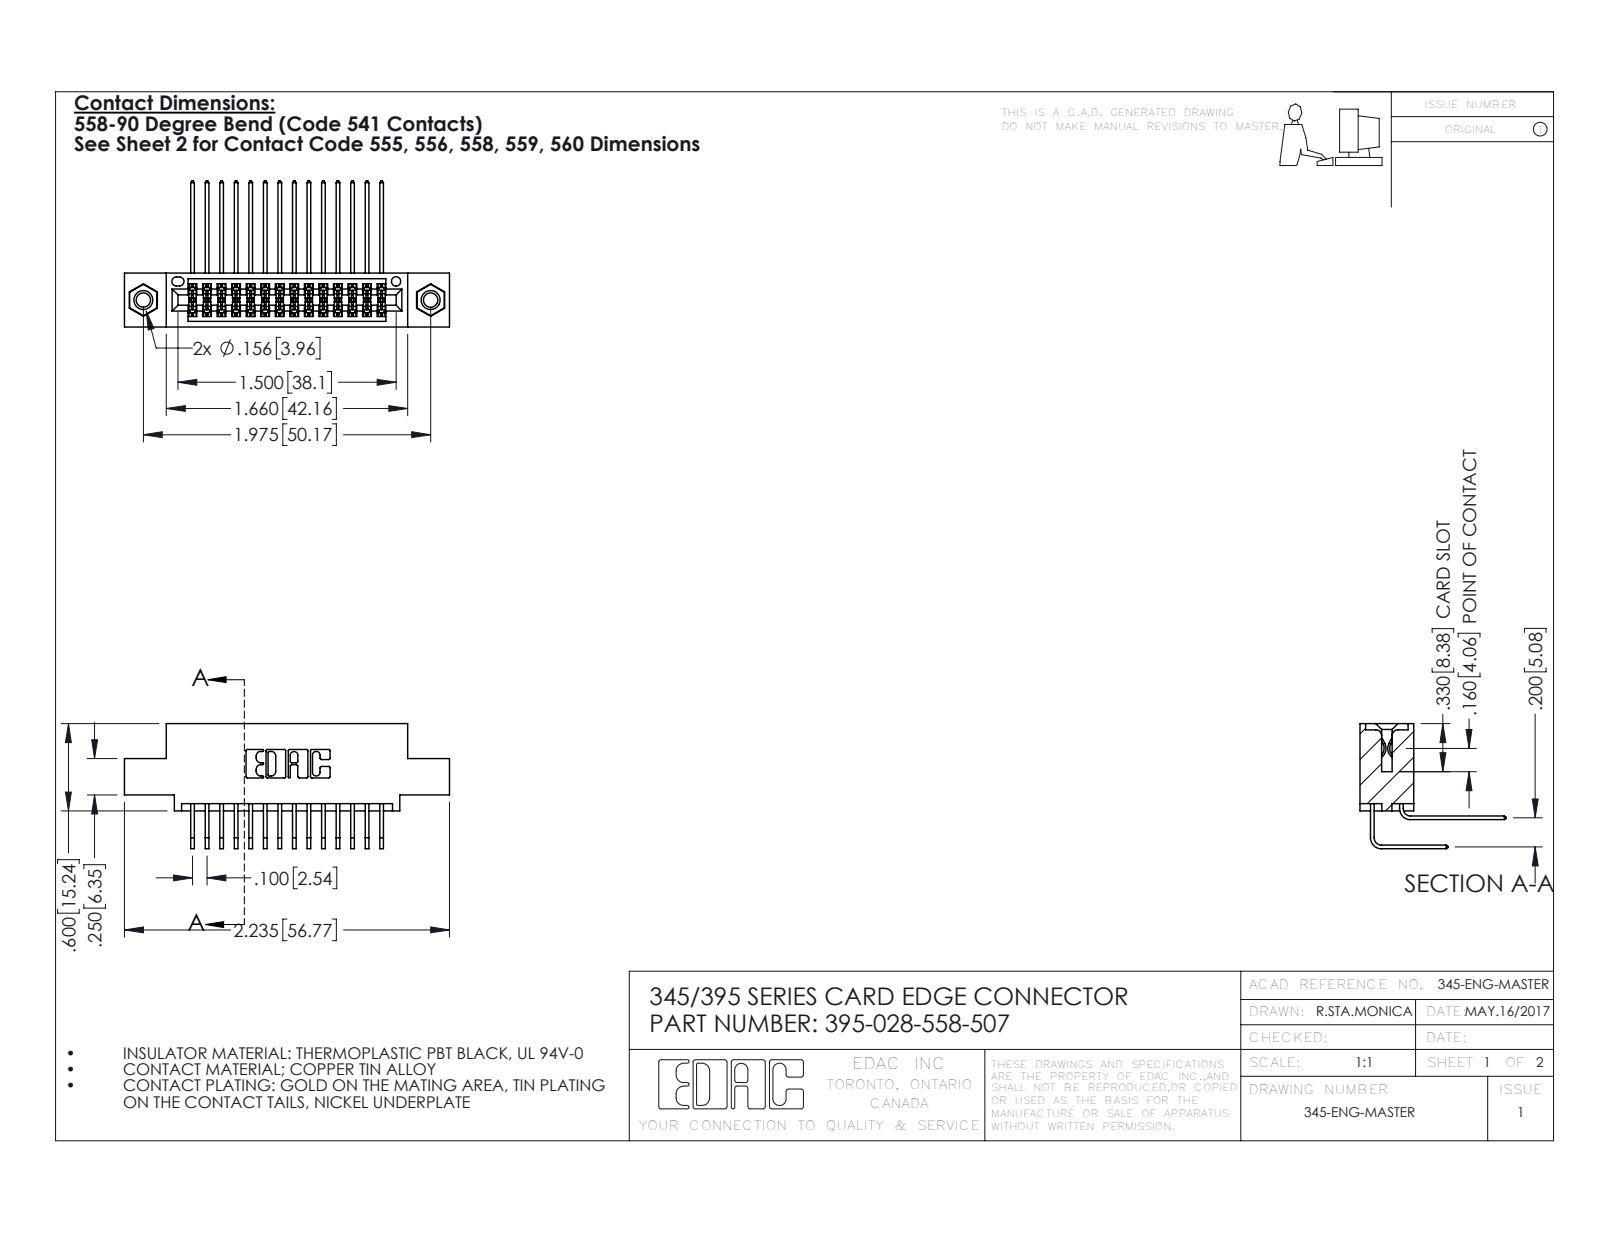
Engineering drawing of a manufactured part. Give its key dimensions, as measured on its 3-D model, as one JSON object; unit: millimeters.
{"part_name": "345-292-001_558 Tail - 2; 395-028-558-507; 345-250-001_345-250-005-103; 345-292-001_558 559 Tail - 1 (+1 more)", "step_written_by": "SolidWorks 2016 (CONFIG_CONTROL_DESIGN)", "units": "millimeters", "bodies": {"solids": 31, "faces": 1646, "planar": 1096, "cylindrical": 534, "other": 16}, "overall_size": [56.8, 25.5, 21.8], "volume_mm3": 5330, "surface_area_mm2": 8213, "round_holes": [[2.5, 2], [3.2, 2], [4, 2], [1.6, 1]], "round_bosses_or_shafts": [[3.9, 2]], "partial_cylinders_radius": [[0.2, 43], [0.3, 22], [0.2, 6], [0.8, 6], [0.7, 3], [0.4, 2], [0.5, 2], [0.6, 2]], "face_to_face_distances": [5.1, 1.8, 7.6, 9.4, 2.5, 6.9, 0.6, 5.7, 2.5, 0.6], "hole_center_spacings": [6.9, 44.2, 50.2]}
